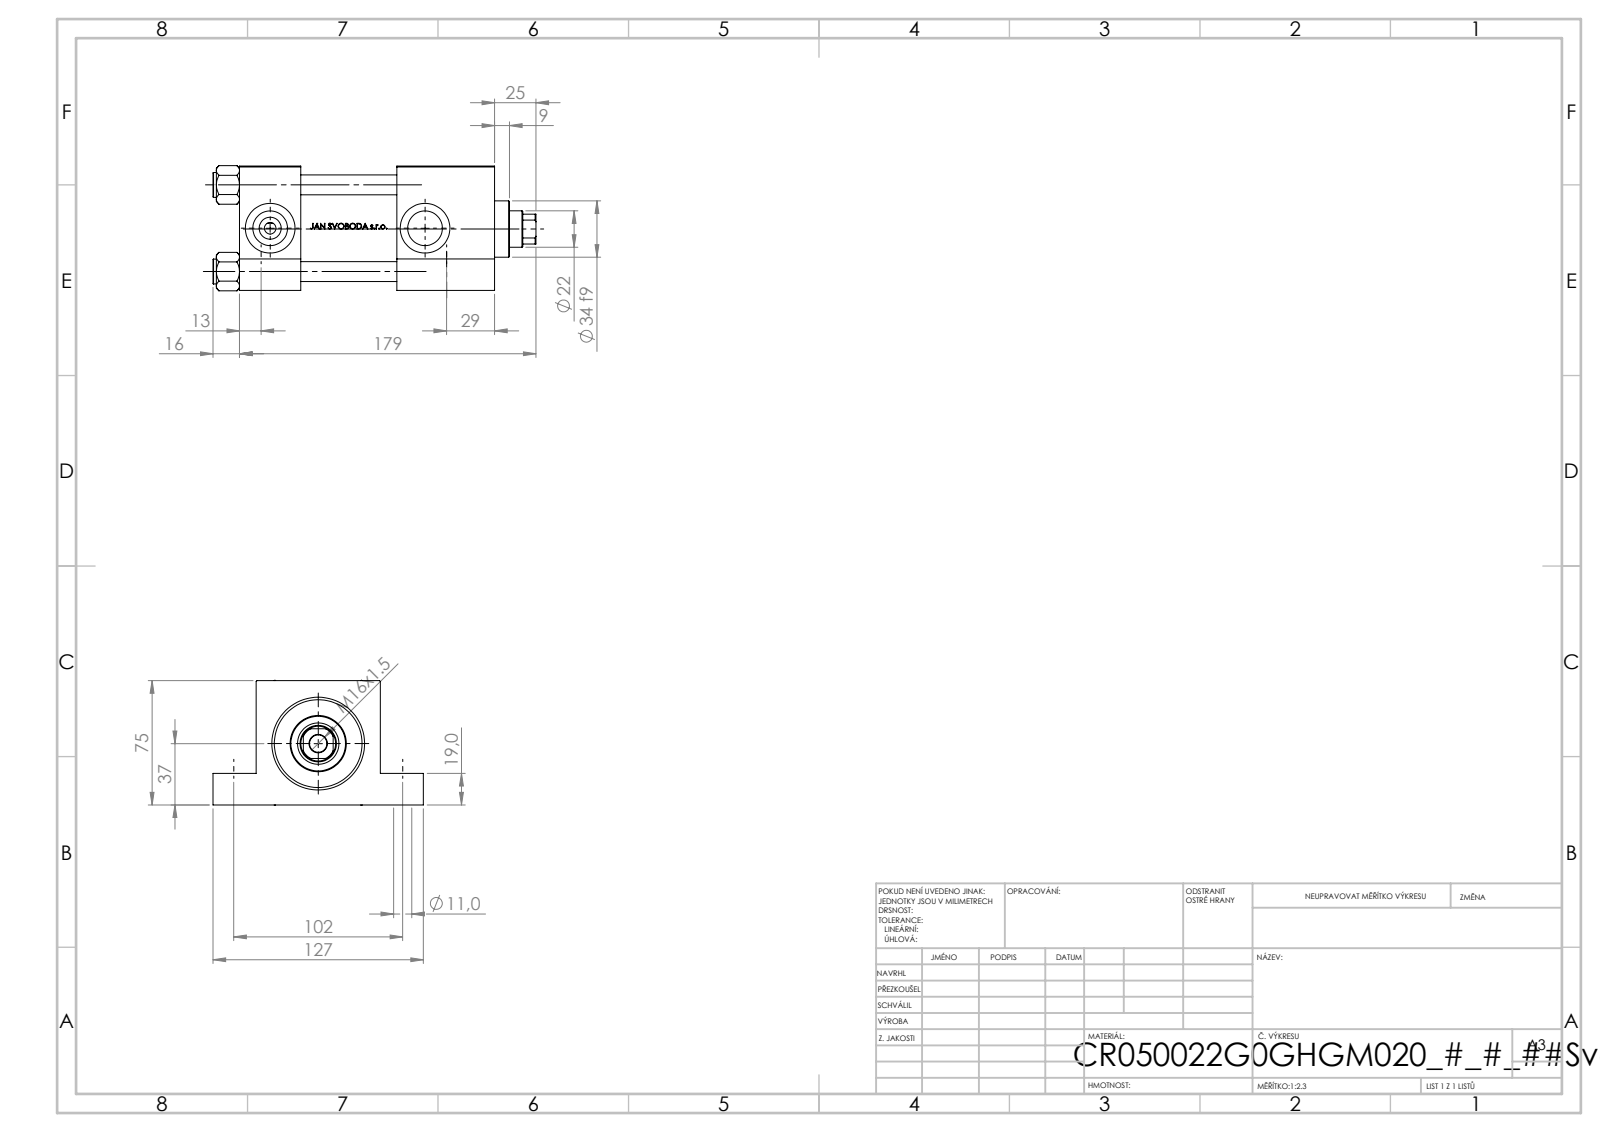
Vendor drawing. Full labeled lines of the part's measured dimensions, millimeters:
Part name (STEP PRODUCT): V215_VC_A; V215CR_VCP_G; V215CR_G_TYCINKA; NUT_M5_G (+1 more)
STEP written by: SolidWorks 2019 (CONFIG_CONTROL_DESIGN)
Units: millimetres
Bodies: 11 solids, 1087 faces (431 planar, 124 cylindrical, 532 other)
Overall size (bounding box): 195 × 127 × 75.54
Volume: 755 848 mm³ · Surface area: 159 324 mm²
Round holes (diameter × count): ⌀12 ×4, ⌀11 ×3, ⌀7 ×2, ⌀20.96 ×2, ⌀30 ×2, ⌀10.5 ×1, ⌀11 ×1, ⌀22 ×1, ⌀25 ×1, ⌀41 ×1, ⌀50 ×1, ⌀53 ×1
Round bosses / shafts (diameter × count): ⌀15 ×4, ⌀56 ×1, ⌀34 ×1
Partial cylindrical surfaces — rounded edges, fillets, slot ends (radius × count): R10.5 ×1
Main face-to-face distances: 75, 37, 154, 117, 19, 56, 95, 58, 59, 26
Hole centre spacings: 52.3, 36.63, 37.34, 73.96, 102, 112, 151.49, 93.5
